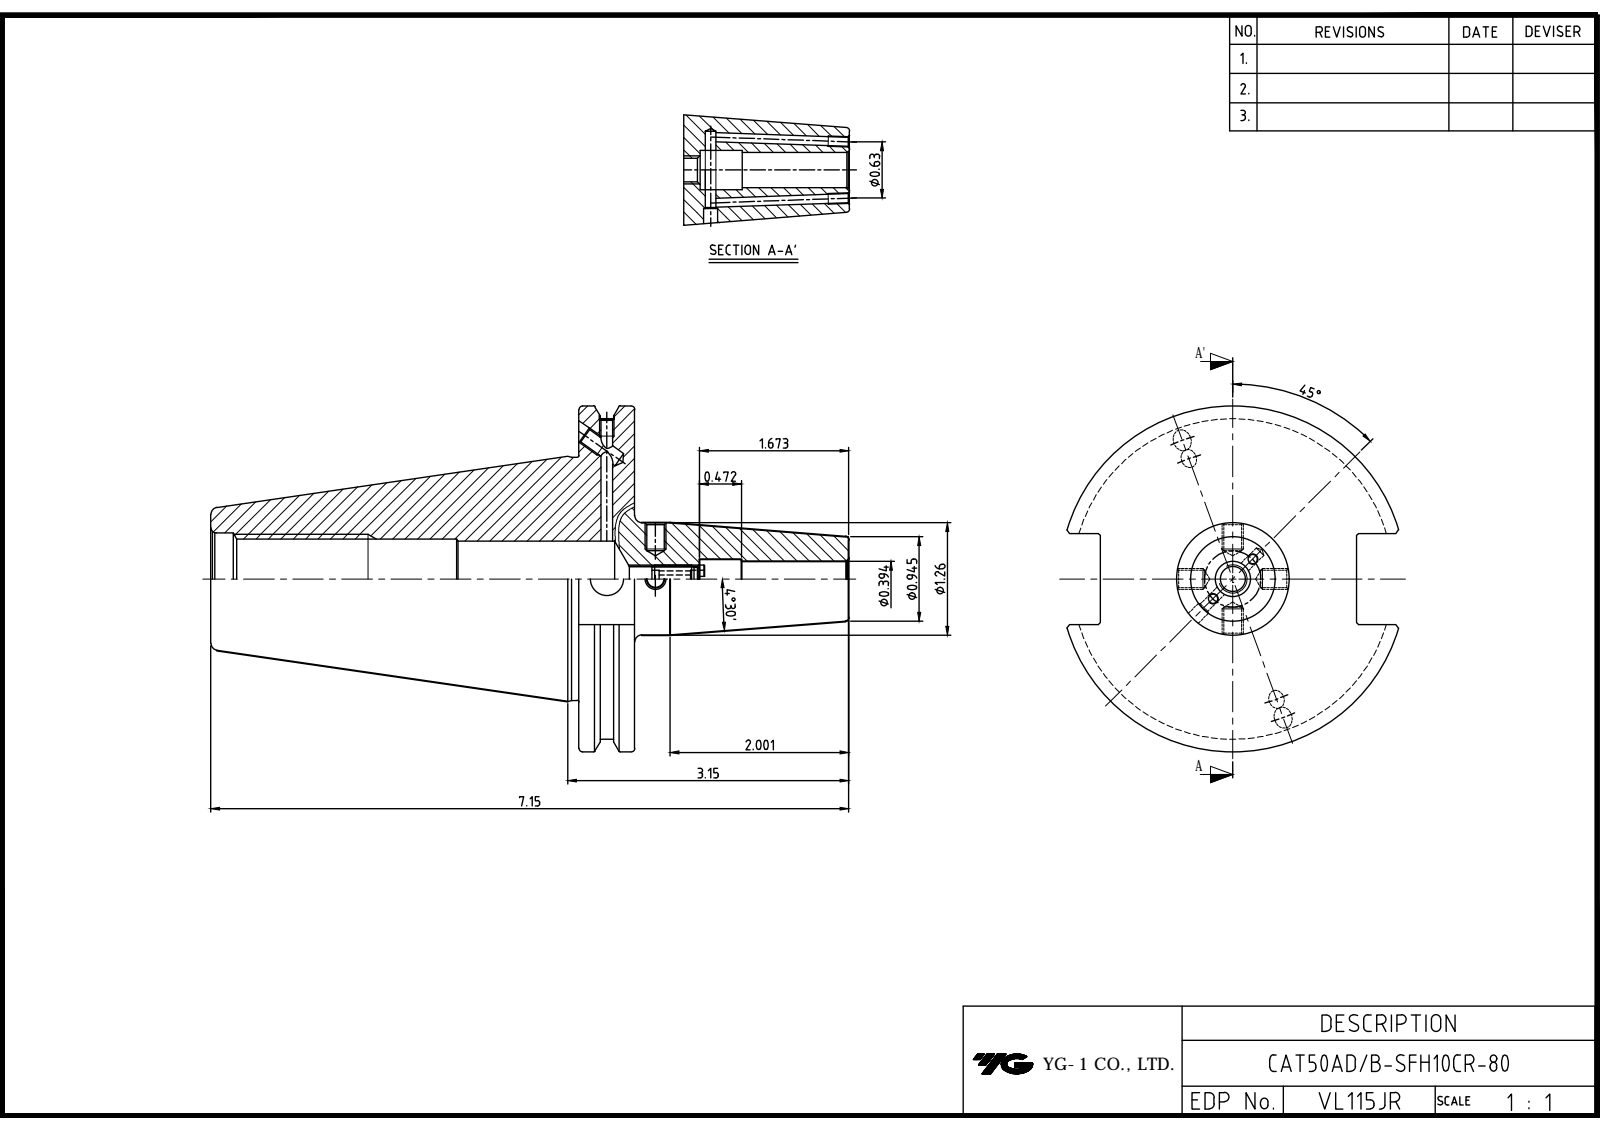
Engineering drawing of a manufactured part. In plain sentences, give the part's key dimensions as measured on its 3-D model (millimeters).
The part is named "CAT50ADB-SFH10CR-80(20231024)". Its 3-D file was written by "Autodesk Inventor 2024 (AUTOMOTIVE_DESIGN)". It is 1 solid with 90 faces: 37 planar, 29 cylindrical and 24 other. Overall it measures 181.6 by 98.42 by 94.69 millimeters. Its volume is 355 222 cubic millimeters and its surface area 52 288 square millimeters. Round holes: 2 of diameter 2.46, 2 of diameter 3.24, 2 of diameter 4.13, 2 of diameter 4.2, 2 of diameter 5, 1 of diameter 6.65, 1 of diameter 9.53, 1 of diameter 10, 1 of diameter 11.2, 1 of diameter 21.5, 1 of diameter 21.97, 1 of diameter 26.2. Round bosses or shafts: 1 of diameter 98.42, 1 of diameter 91.29, 1 of diameter 69.25, 1 of diameter 32. The main face-to-face distances are 15.88, 104.77, 120.65, 73.03, 25.9, 181.6, 76.83, 60.95, 114.64, 9.87.
